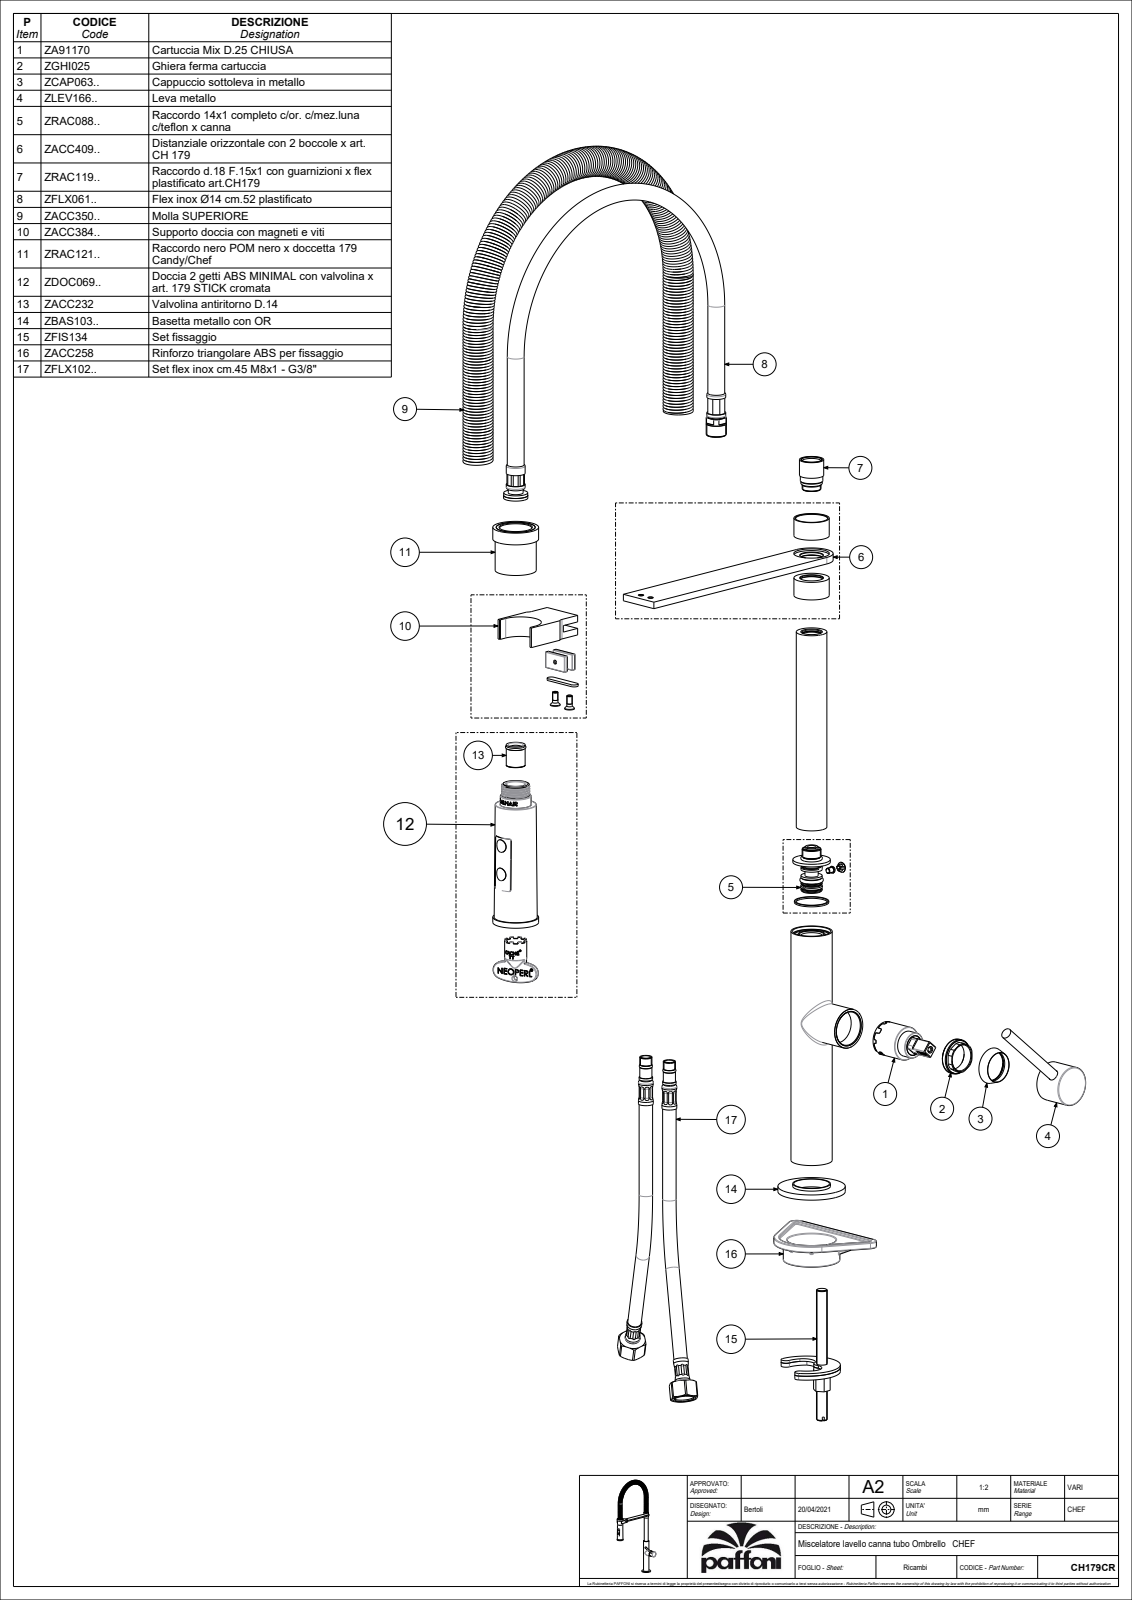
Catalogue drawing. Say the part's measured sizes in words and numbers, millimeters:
The part is named "CH179CR". Its 3-D file was written by "CREO PARAMETRIC BY PTC INC, 2020044 (CONFIG_CONTROL_DESIGN)". It is 2 solids with 2977 faces: 1273 planar, 1027 cylindrical and 677 other. Overall it measures 556.85 by 252.5 by 88.53 millimeters. Its volume is 296 338 cubic millimeters and its surface area 233 562 square millimeters. Round holes: 172 of diameter 0.5, 6 of diameter 5, 3 of diameter 3, 2 of diameter 7, 2 of diameter 8.8, 2 of diameter 9.9, 2 of diameter 13, 2 of diameter 15, 2 of diameter 23.7, 2 of diameter 27.5, 1 of diameter 4, 1 of diameter 5.2. Round bosses or shafts: 16 of diameter 0.7, 2 of diameter 9.5, 2 of diameter 7.6, 2 of diameter 7.3, 2 of diameter 5.5, 1 of diameter 50, 1 of diameter 42, 1 of diameter 34. Partial cylindrical surfaces (rounded edges, fillets, slot ends): 62 of radius 0.5, 42 of radius 0.25, 40 of radius 0.3, 35 of radius 1, 21 of radius 0.2, 12 of radius 2, 10 of radius 0.15, 6 of radius 5. The main face-to-face distances are 5, 10, 1.5, 4, 326.4, 331.4, 32, 330.4, 335.4, 340.4. The hole center spacings are 0.7, 1.39, 1.4, 1.83, 2.08, 4.56, 5.02, 7.87.
